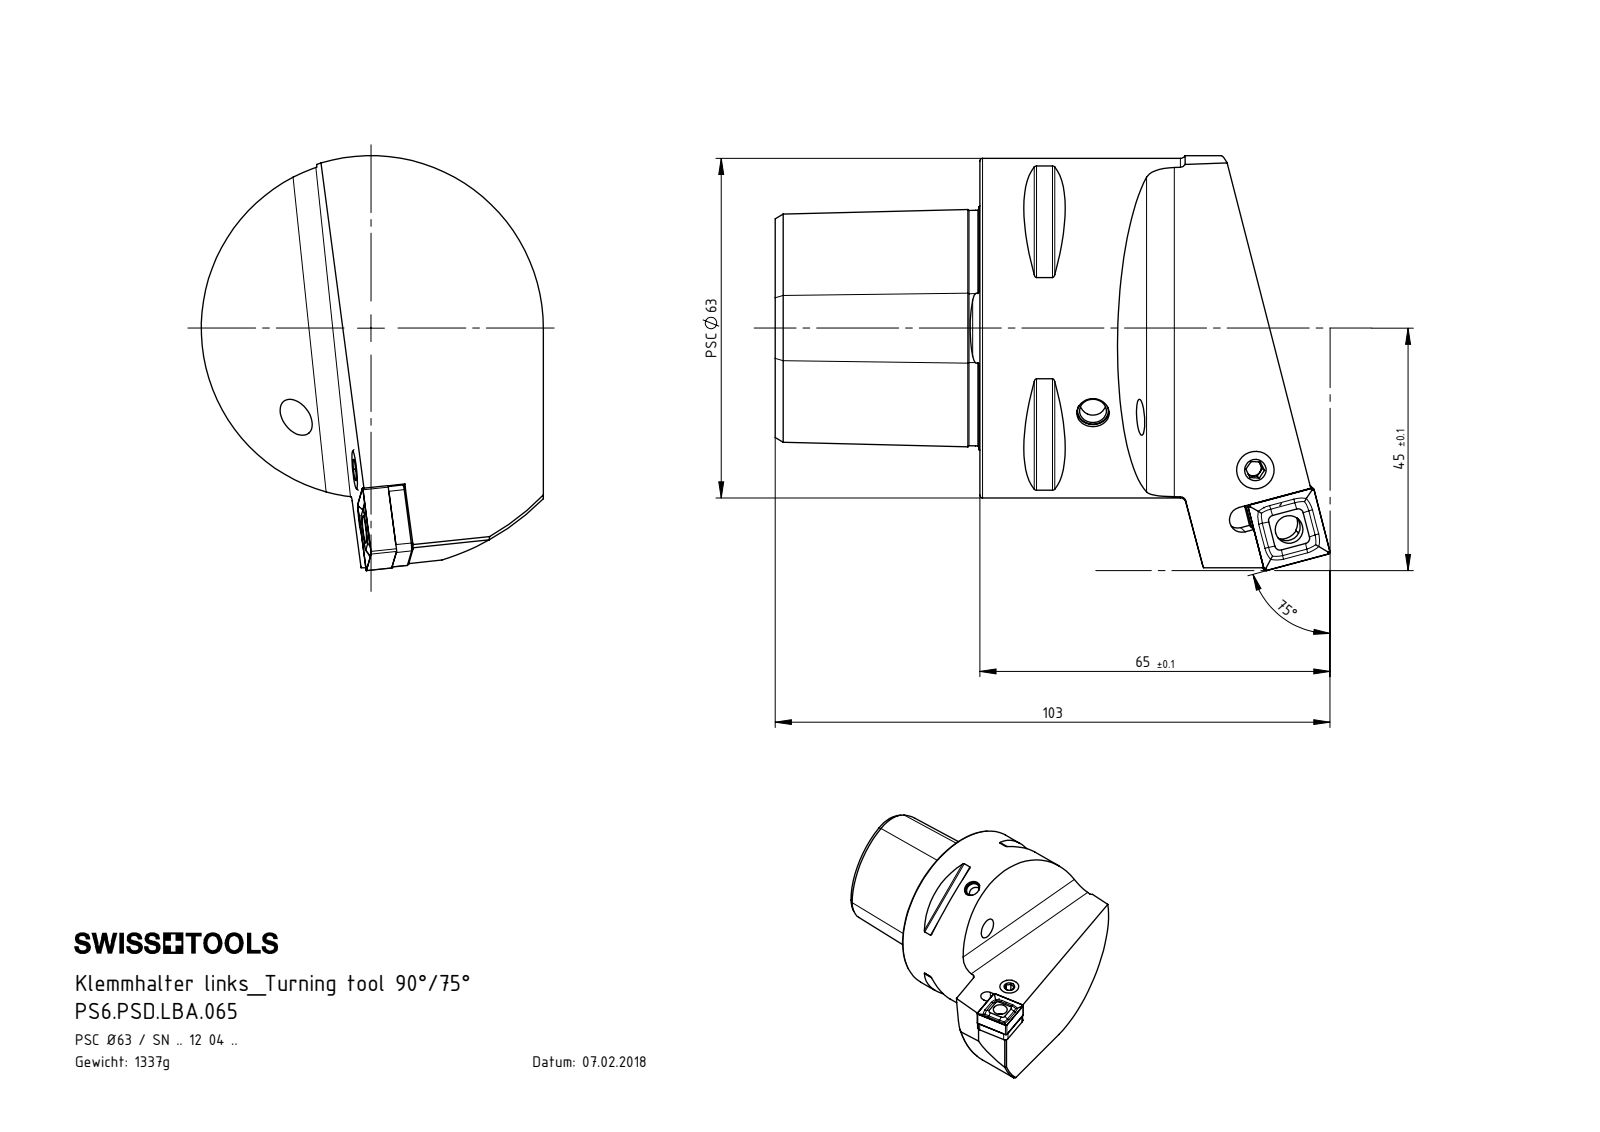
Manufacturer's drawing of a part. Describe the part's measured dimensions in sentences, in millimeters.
The part is named "PS6.PSD.LBA.065; KVT_MB_600_060; SNMG120404; WCD-ER1.101.000 (+4 more)". Its 3-D file was written by "SolidWorks 2017 (AUTOMOTIVE_DESIGN)". It is 8 solids with 340 faces: 89 planar, 83 cylindrical and 168 other. Overall it measures 103 by 77 by 63.5 millimeters. Its volume is 169 841 cubic millimeters and its surface area 31 276 square millimeters. Round holes: 2 of diameter 5, 2 of diameter 6.4, 1 of diameter 4, 1 of diameter 5.16, 1 of diameter 7, 1 of diameter 8.1, 1 of diameter 8.4, 1 of diameter 18, 1 of diameter 28, 1 of diameter 32. Round bosses or shafts: 1 of diameter 63, 1 of diameter 8, 1 of diameter 7.9, 1 of diameter 6.4, 1 of diameter 6, 1 of diameter 4.5, 1 of diameter 3.55. Partial cylindrical surfaces (rounded edges, fillets, slot ends): 8 of radius 0.5, 4 of radius 0.4, 4 of radius 1.2, 2 of radius 2.5, 2 of radius 6, 1 of radius 2.2, 1 of radius 2.35, 1 of radius 2.8. The main face-to-face distances are 38, 24.88, 27, 11, 3.18, 55.8, 12.23, 4.47, 12.21, 37.8. The hole center spacings are 12.8, 12.81, 27.5.
